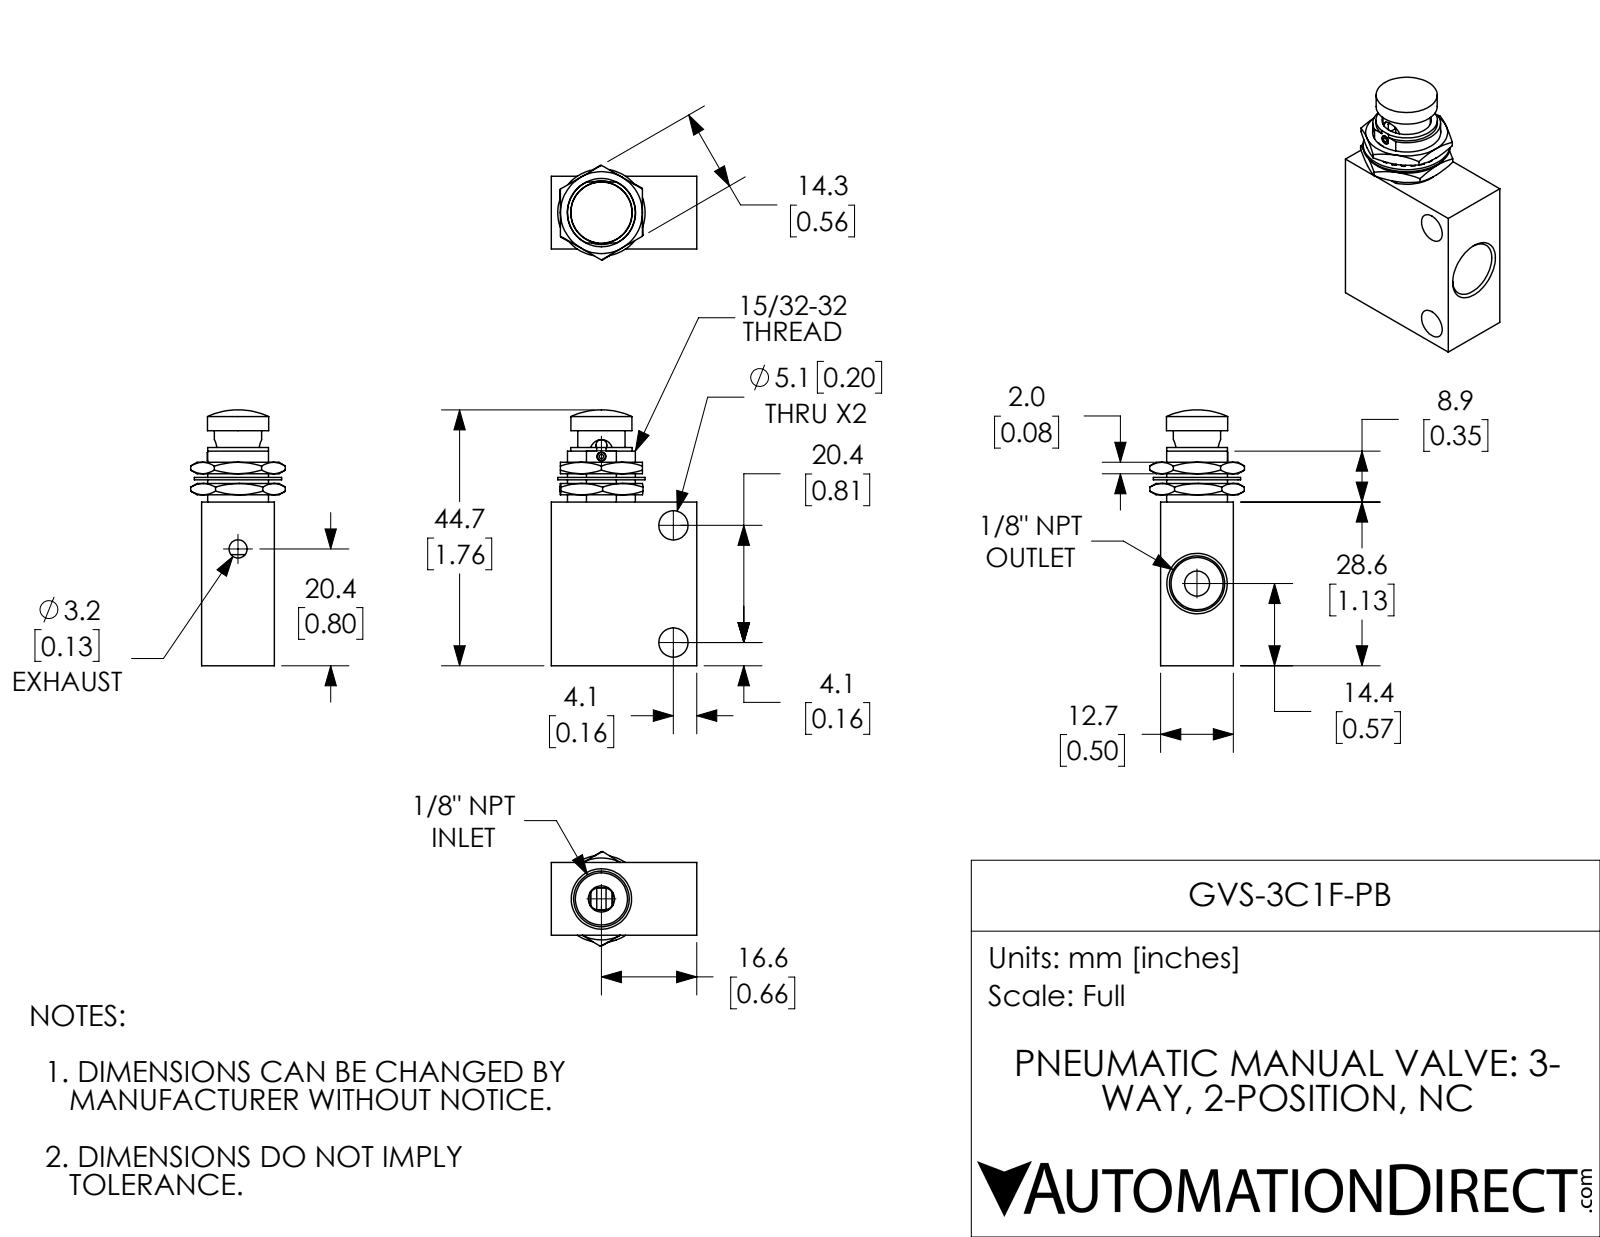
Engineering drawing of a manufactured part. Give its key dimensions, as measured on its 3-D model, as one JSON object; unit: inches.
{"part_name": "GVS-3C1F-PB", "step_written_by": "SolidWorks 2018 (AUTOMOTIVE_DESIGN)", "units": "inches", "bodies": {"solids": 6, "faces": 254, "planar": 101, "cylindrical": 95, "other": 58}, "overall_size": [1.759, 1, 0.65], "volume_in3": 0.485, "surface_area_in2": 9.451, "round_holes": [[0.201, 2], [0.03, 1], [0.063, 1], [0.125, 1], [0.153, 1], [0.172, 1], [0.18, 1], [0.182, 1], [0.25, 1], [0.34, 1], [0.438, 1]], "round_bosses_or_shafts": [[0.6, 1], [0.423, 1], [0.42, 1], [0.325, 1], [0.063, 1]], "partial_cylinders_radius": [[0.037, 2], [0.233, 1], [0.239, 1], [0.26, 1]], "face_to_face_distances": [0.5, 1, 1.125, 0.145, 0.078, 0.041, 0.459, 0.103, 0.025, 1.295], "hole_center_spacings": [0.039, 0.238, 0.685, 0.713, 0.805, 1.37, 1.407]}
